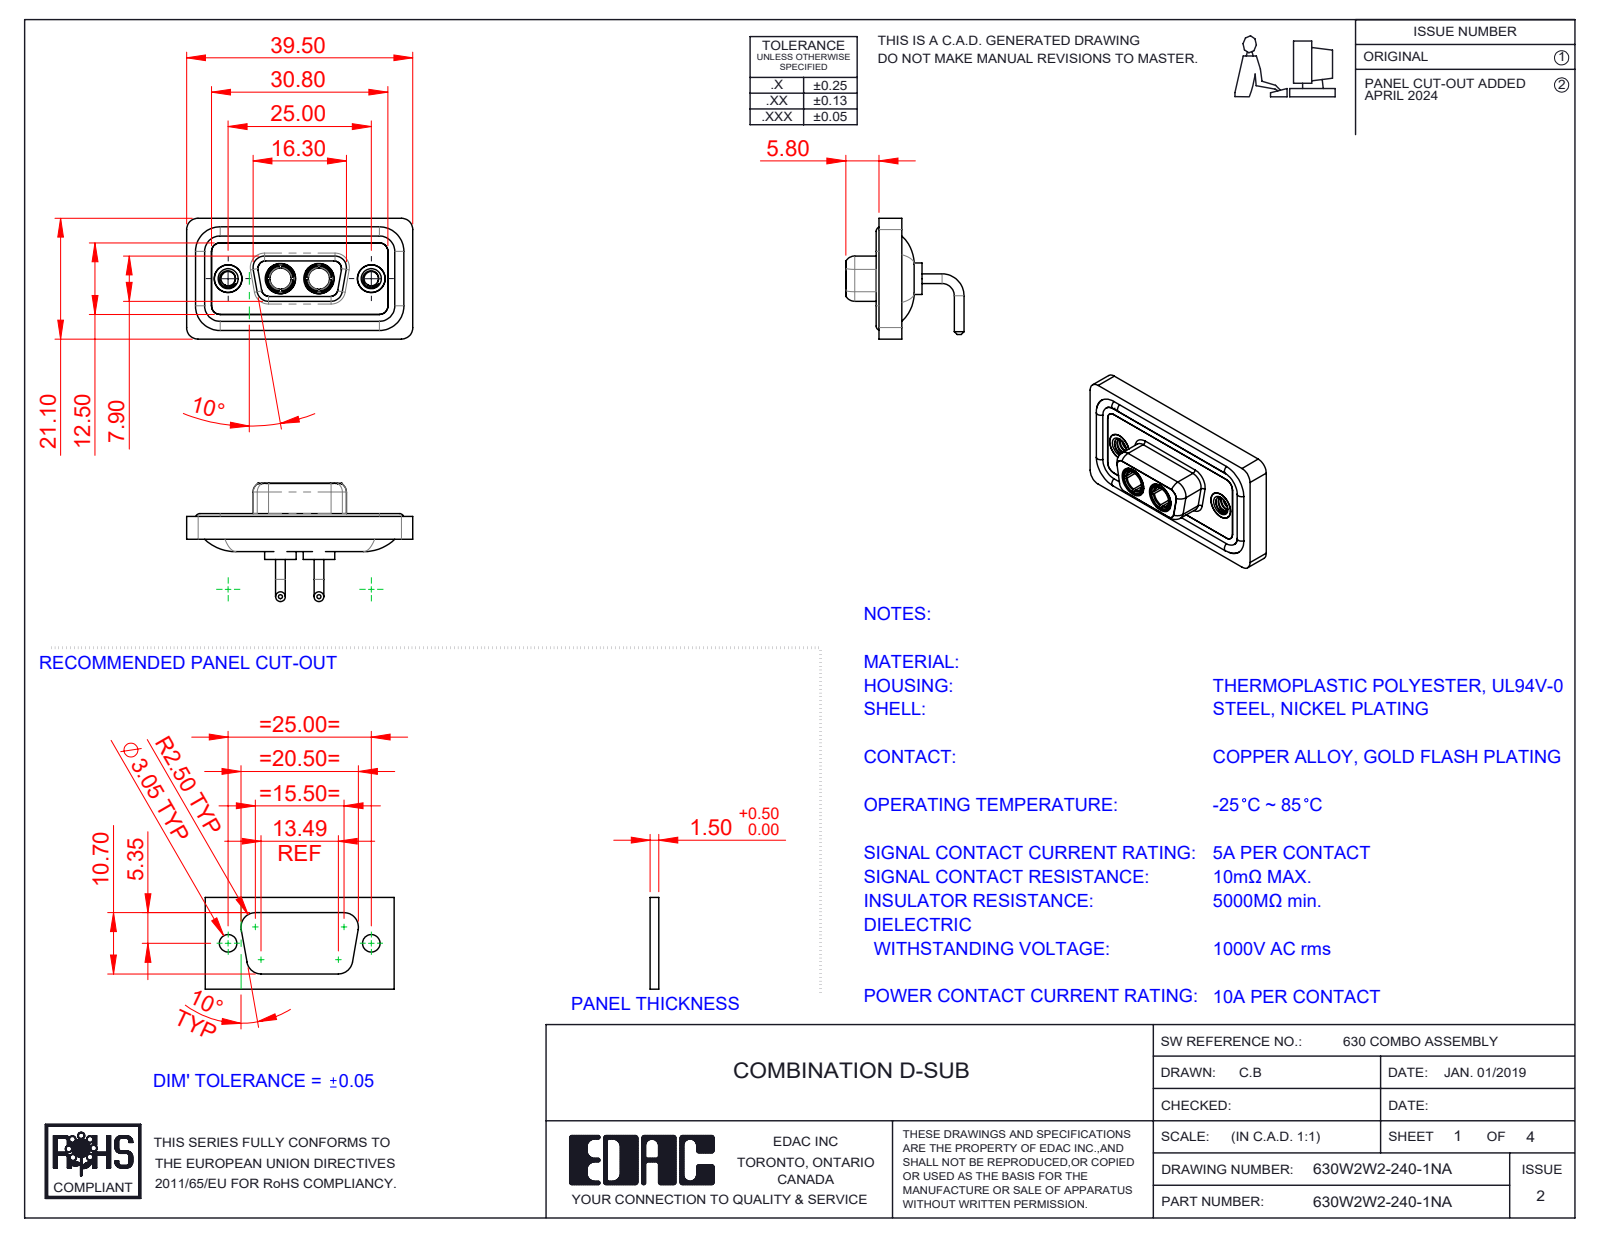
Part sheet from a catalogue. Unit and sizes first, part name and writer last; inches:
Units: inches
Overall size (bounding box): 1.555 × 0.831 × 0.813
Round holes (diameter × count): ⌀0.191 ×4, ⌀0.098 ×2, ⌀0.146 ×2, ⌀0.157 ×2, ⌀0.159 ×2, ⌀0.197 ×2, ⌀0.209 ×2
Round bosses / shafts (diameter × count): ⌀0.067 ×4, ⌀0.063 ×4, ⌀0.217 ×2, ⌀0.205 ×2, ⌀0.195 ×2, ⌀0.195 ×2, ⌀0.189 ×2, ⌀0.187 ×2
Partial cylindrical surfaces — rounded edges, fillets, slot ends (radius × count): R0.059 ×18, R0.079 ×18, R0.053 ×8, R0.063 ×8, R0.01 ×4, R0.02 ×4, R0.024 ×4, R0.026 ×4
Main face-to-face distances: 0.016, 0.071, 0.043, 0.114, 0.098, 0.063, 0.122, 0.059, 0.083, 0.157
Hole centre spacings: 0.36, 0.624, 0.265, 0.984
Volume: 0.286 in³ · Surface area: 11.91 in²
Bodies: 11 solids, 536 faces (163 planar, 236 cylindrical, 137 other)
Part name (STEP PRODUCT): 630Combo Threaded Rivet_A; Power Socket_10A RA; 630Combo Waterproof Housing_09 Contacts; 630Combo Housing_2W2 (+3 more)
STEP written by: SolidWorks 2023 (CONFIG_CONTROL_DESIGN)
